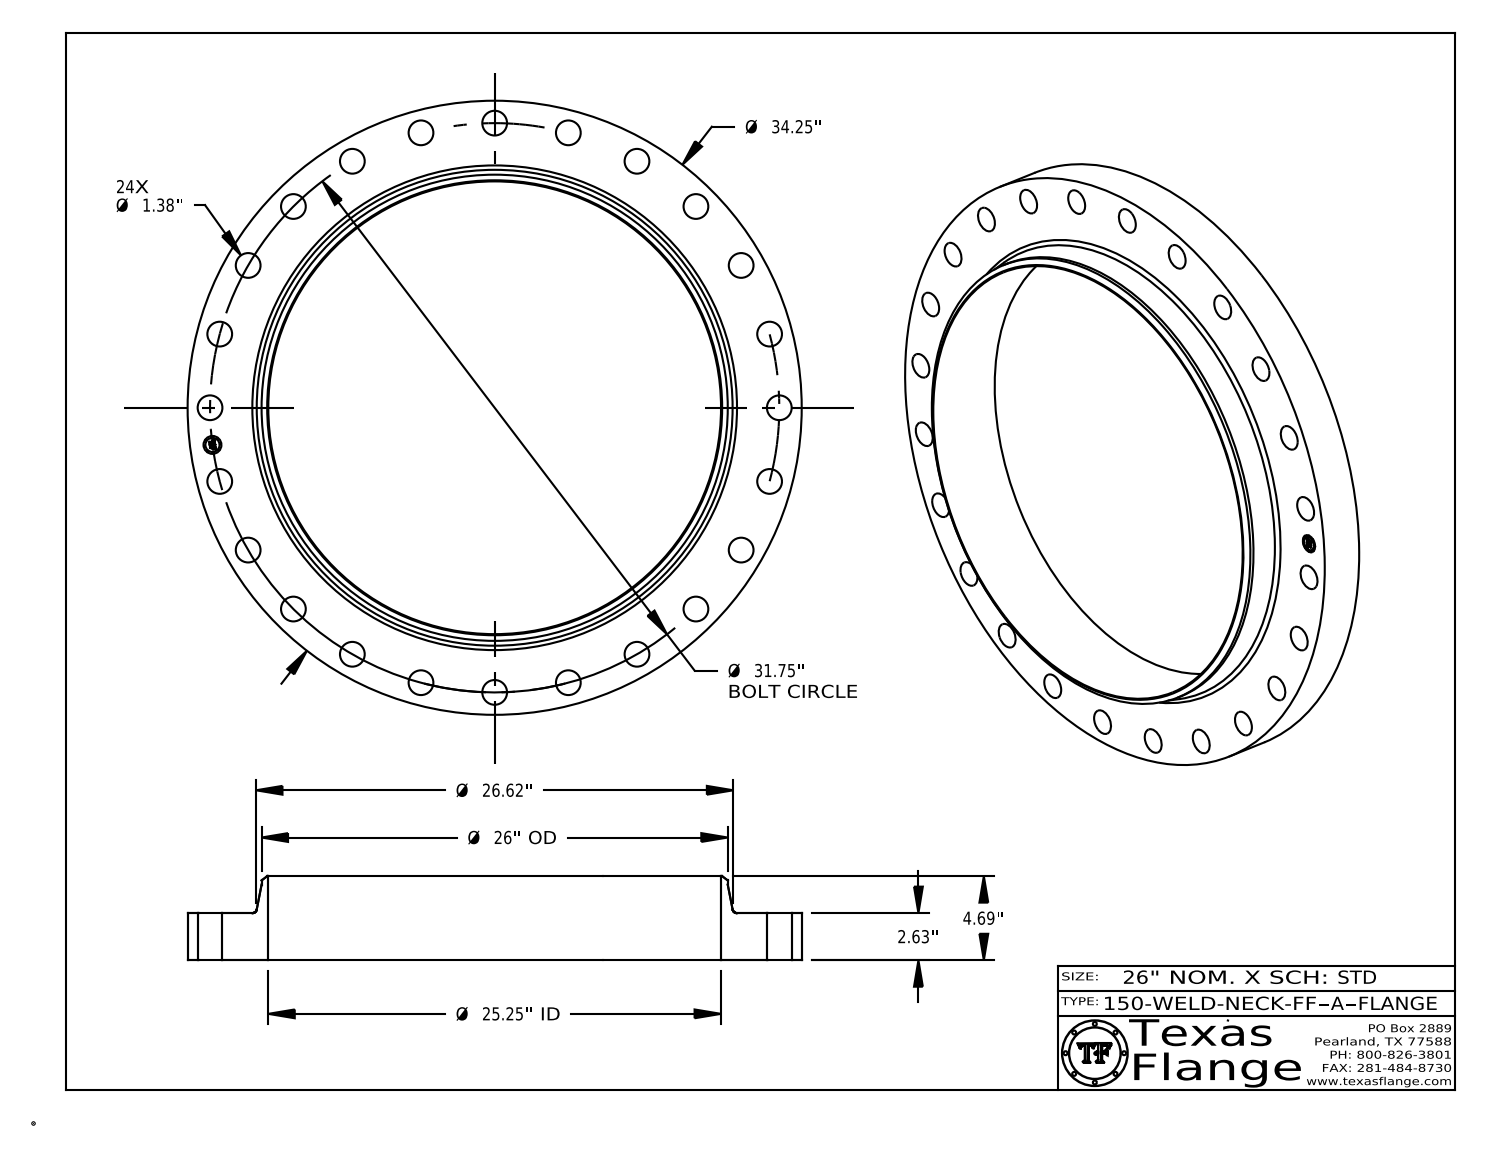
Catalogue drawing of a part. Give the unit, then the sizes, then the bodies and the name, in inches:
Units: inches
Overall size (bounding box): 34.25 × 34.25 × 4.69
Round holes (diameter × count): ⌀1.38 ×24, ⌀1 ×1, ⌀25.25 ×1
Round bosses / shafts (diameter × count): ⌀0.061 ×8, ⌀34.25 ×1, ⌀26 ×1, ⌀0.788 ×1
Main face-to-face distances: 2.63, 4.69, 2.06, 2.615, 0.015, 2.075, 0.298, 0.292, 0.054, 0.193
Hole centre spacings: 15.875, 15.875, 29.333, 27.496, 4.144, 8.217, 12.15, 19.328
Volume: 1 092 in³ · Surface area: 1 826 in²
Bodies: 1 solid, 448 faces (368 planar, 74 cylindrical, 6 other)
Part name (STEP PRODUCT): 150-WELD-NECK-FF, Series A
STEP written by: CATIA V5 STEP AP214 (AUTOMOTIVE_DESIGN)
